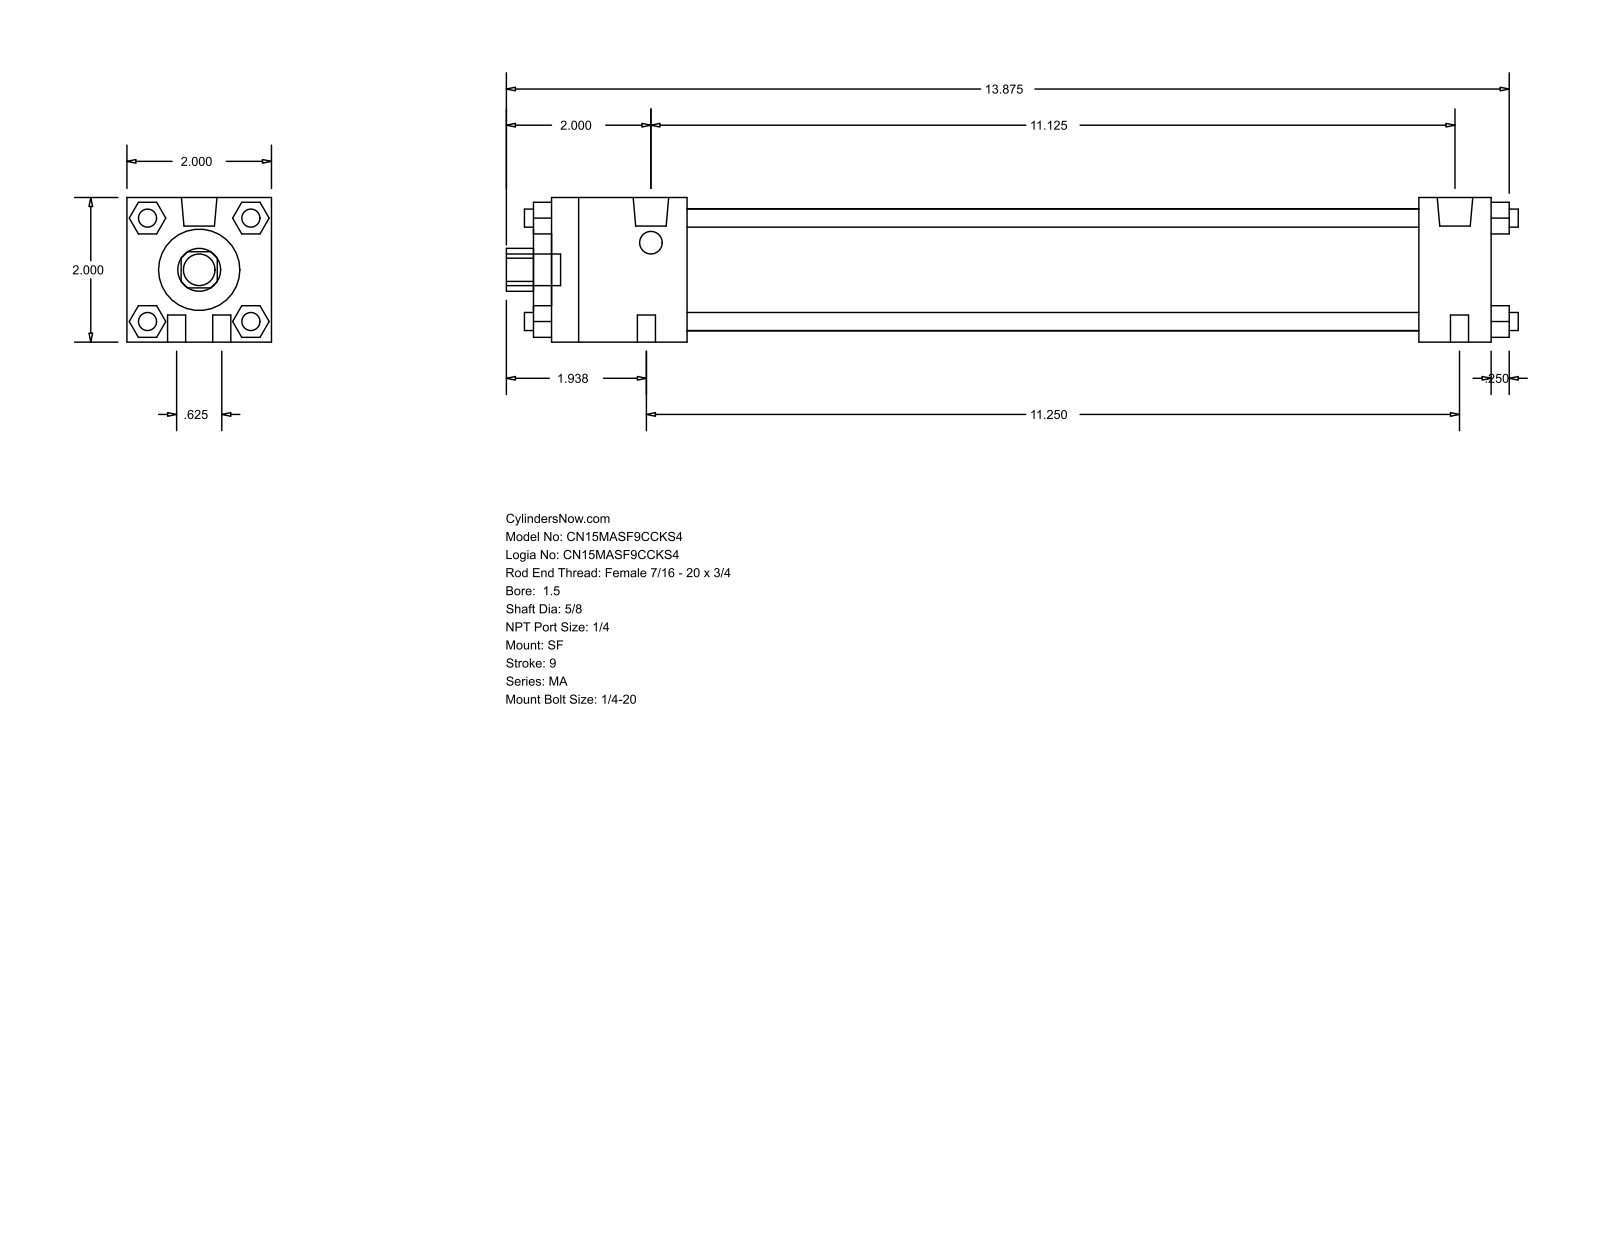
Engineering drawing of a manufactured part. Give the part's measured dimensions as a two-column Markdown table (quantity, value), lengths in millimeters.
| quantity | value |
| --- | --- |
| part name | MA_SF__0150_0.625 |
| STEP written by | GSSL Pune (CONFIG_CONTROL_DESIGN) |
| units | millimeters |
| bodies | 0 solids, 124 faces (94 planar, 30 cylindrical, 0 other) |
| overall size | 355.6 × 50.8 × 50.8 |
| round holes (diameter × count) | 15.88 × 1, 28.57 × 1, 42.93 × 1 |
| round bosses / shafts (diameter × count) | 6.35 × 8, 12.49 × 2, 7.94 × 2, 11.11 × 1 |
| partial cylindrical surfaces (radius × count) | 7.54 × 1 |
| main face-to-face distances | 50.8, 330.19, 47.62, 304.8, 257.18, 282.57, 25.39, 6.35, 53.97, 311.15 |
